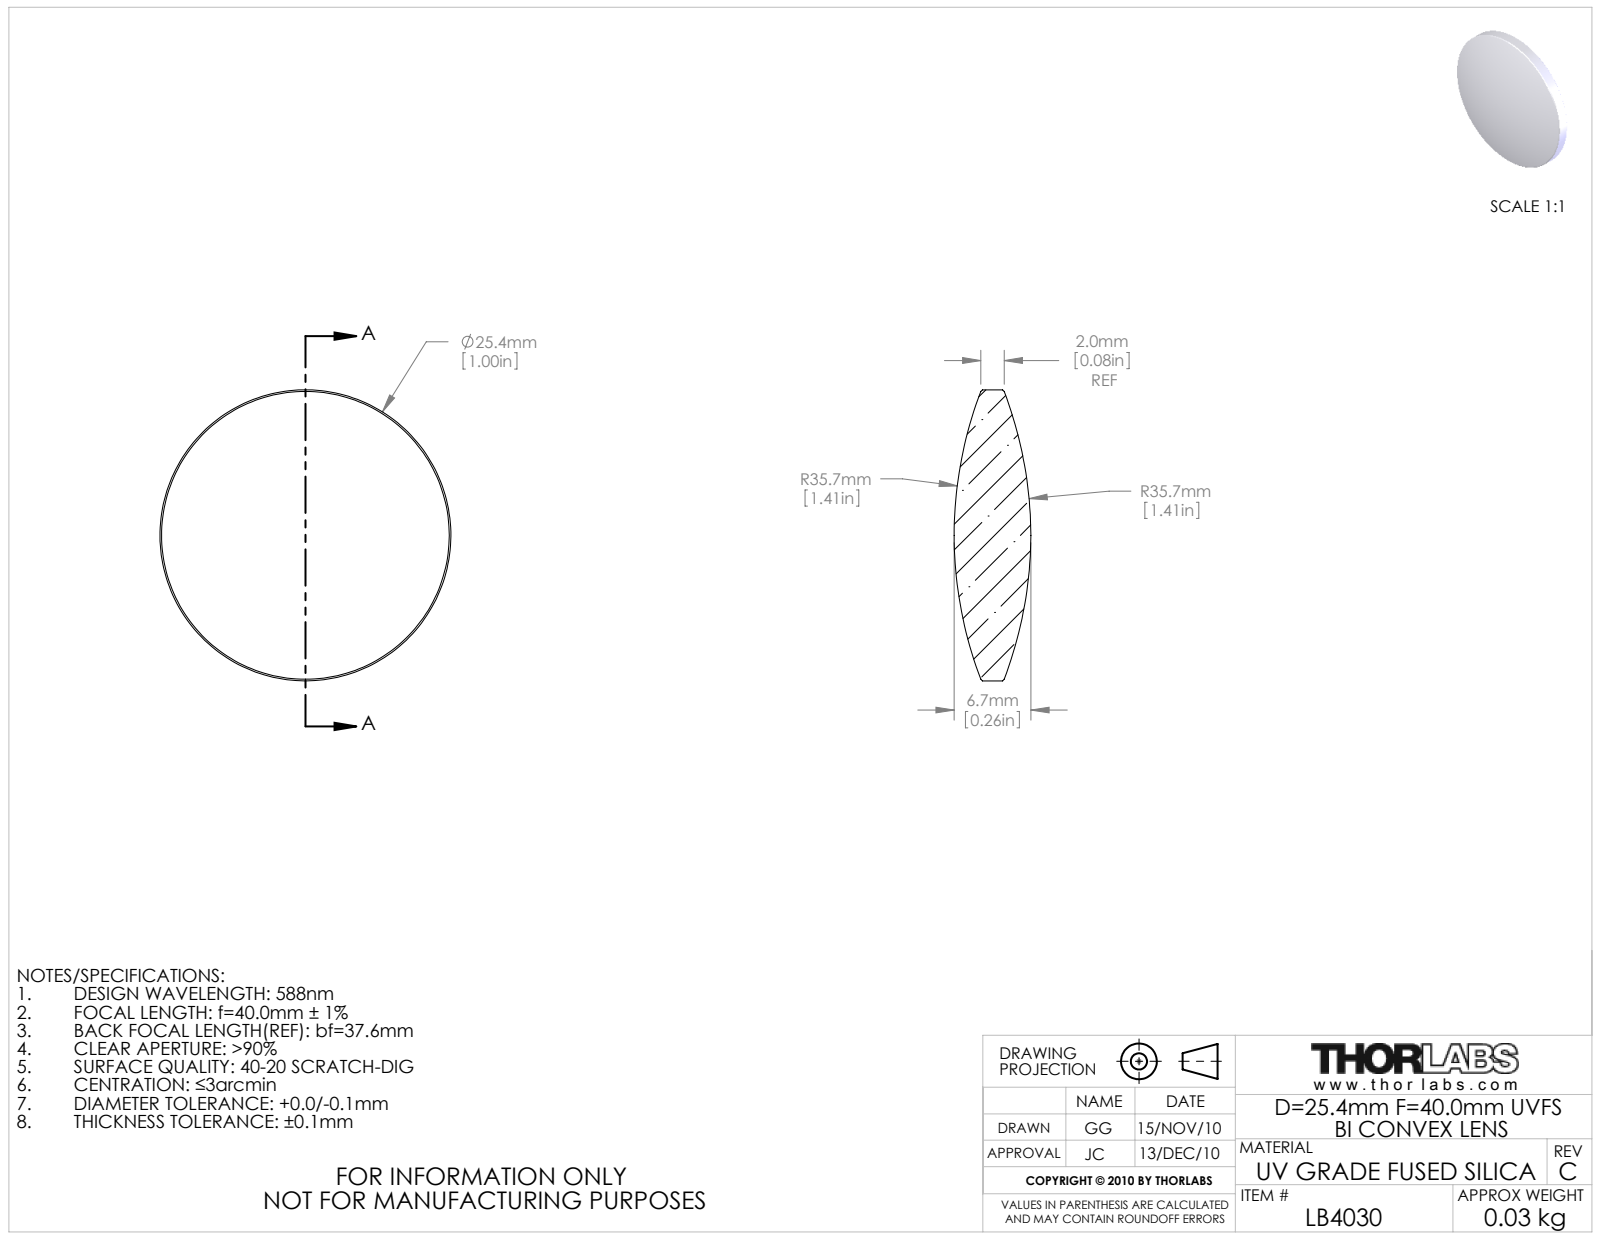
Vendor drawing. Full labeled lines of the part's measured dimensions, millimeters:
Part name (STEP PRODUCT): 3400-E0W
STEP written by: SolidWorks 2009 (AUTOMOTIVE_DESIGN)
Units: millimetres
Bodies: 1 solid, 10 faces (0 planar, 2 cylindrical, 8 other)
Overall size (bounding box): 25.4 × 25.4 × 6.7
Volume: 2 192 mm³ · Surface area: 1 197 mm²
Round bosses / shafts (diameter × count): ⌀25.4 ×1
